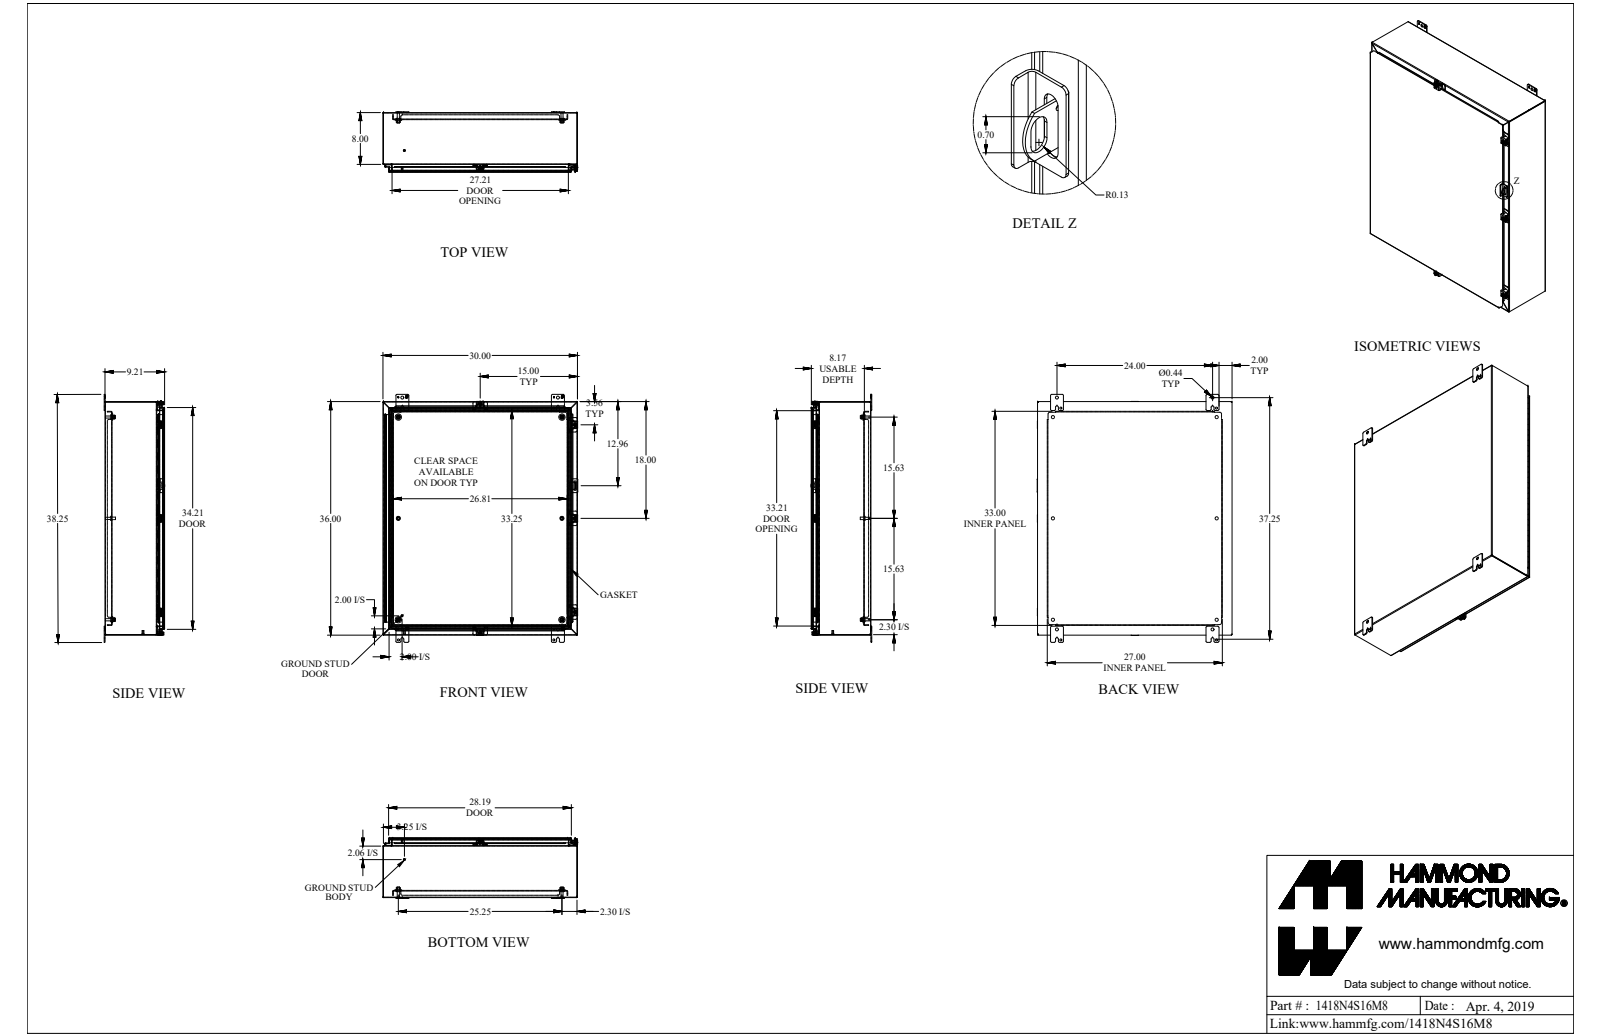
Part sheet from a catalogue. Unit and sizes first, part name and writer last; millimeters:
Units: millimetres
Overall size (bounding box): 971.6 × 763.6 × 238.1
Round holes (diameter × count): ⌀12.7 ×6, ⌀5.4 ×5, ⌀6.7 ×5, ⌀9.5 ×5, ⌀7.8 ×4, ⌀8 ×4, ⌀11.1 ×4, ⌀11.3 ×4, ⌀3.2 ×1, ⌀4.7 ×1
Round bosses / shafts (diameter × count): ⌀16.5 ×6, ⌀9.5 ×6, ⌀8.4 ×6, ⌀12.7 ×5, ⌀9.9 ×5, ⌀6.2 ×5, ⌀25.4 ×4, ⌀8 ×2
Partial cylindrical surfaces — rounded edges, fillets, slot ends (radius × count): R6.4 ×32, R1.2 ×27, R3.6 ×27, R4.8 ×26, R0.9 ×24, R2.7 ×24, R3.2 ×14, R3.6 ×10
Main face-to-face distances: 1.8, 230.3, 232.1, 1.8, 232.1, 2.4, 233.9, 23.8, 25.6, 205.9
Hole centre spacings: 396.9, 553.3, 609.6, 641.4, 754.2, 1093.7, 61.8, 325.2
Volume: 5 968 000 mm³ · Surface area: 6 056 000 mm²
Bodies: 48 solids, 1652 faces (898 planar, 590 cylindrical, 164 other)
Part name (STEP PRODUCT): 1418N4S16M8_Default
STEP written by: SolidWorks 2019 (CONFIG_CONTROL_DESIGN)
